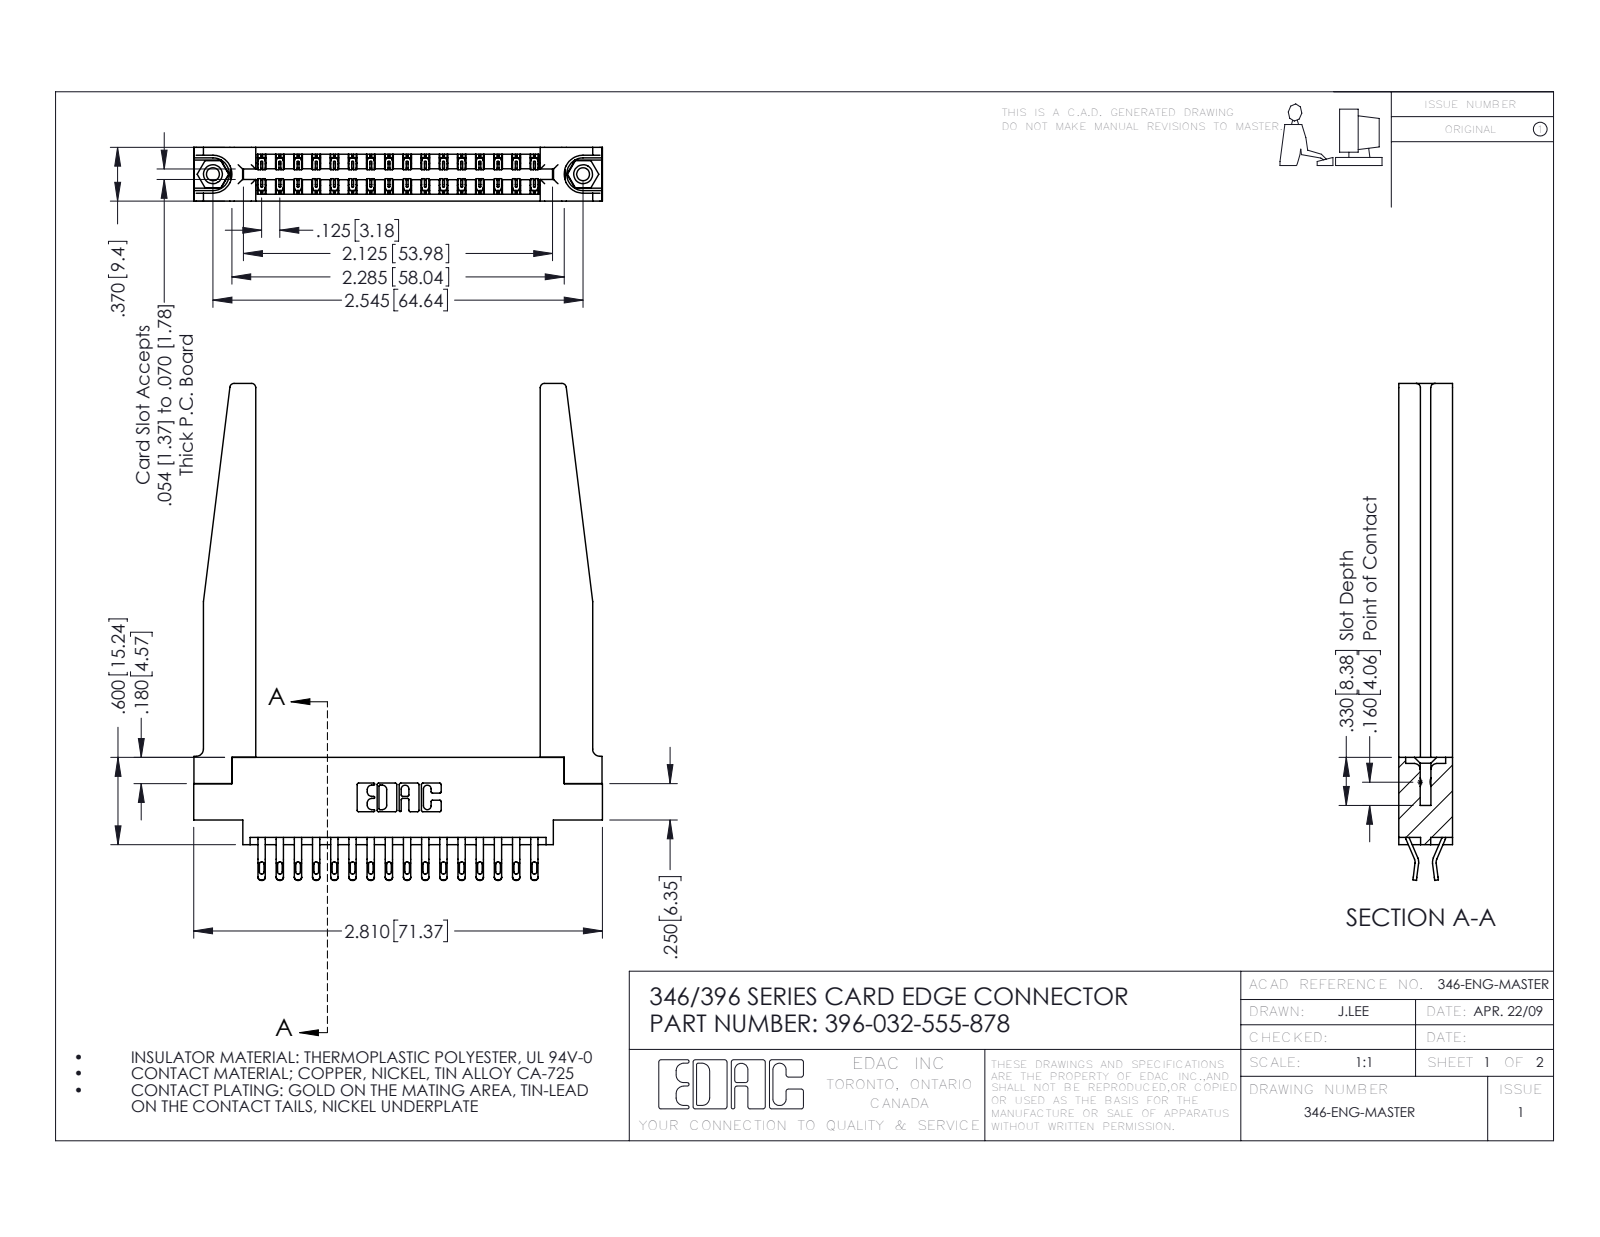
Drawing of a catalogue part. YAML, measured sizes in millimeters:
part_name: "396-032-555-878; 345-250-001_345-250-001-102; 346 Part_0.170 Offset - 0.156 Dia-TH; 346-220-078_345-220-078 (+1 more)"
step_written_by: "SolidWorks 2016 (CONFIG_CONTROL_DESIGN)"
units: millimeters
bodies: {solids: 37, faces: 2216, planar: 1278, cylindrical: 886, other: 52}
overall_size: [86.7, 71.4, 9.4]
volume: 13600
surface_area: 15850
round_holes:
  - {diameter: 2.3, count: 2}
  - {diameter: 3.2, count: 2}
  - {diameter: 4, count: 2}
  - {diameter: 1.6, count: 1}
round_bosses_or_shafts:
  - {diameter: 3.9, count: 2}
partial_cylinders:
  - {radius: 0.4, count: 64}
  - {radius: 0.5, count: 64}
  - {radius: 0.2, count: 48}
  - {radius: 0.3, count: 22}
  - {radius: 0.8, count: 8}
  - {radius: 0.2, count: 6}
  - {radius: 0.8, count: 6}
  - {radius: 1.3, count: 4}
face_to_face_distances: [9.4, 3.8, 1.8, 3.8, 1.2, 8.2, 6.4, 2.6, 5.6, 4.4]
hole_center_spacings: [6.2, 59.4, 64.6]
